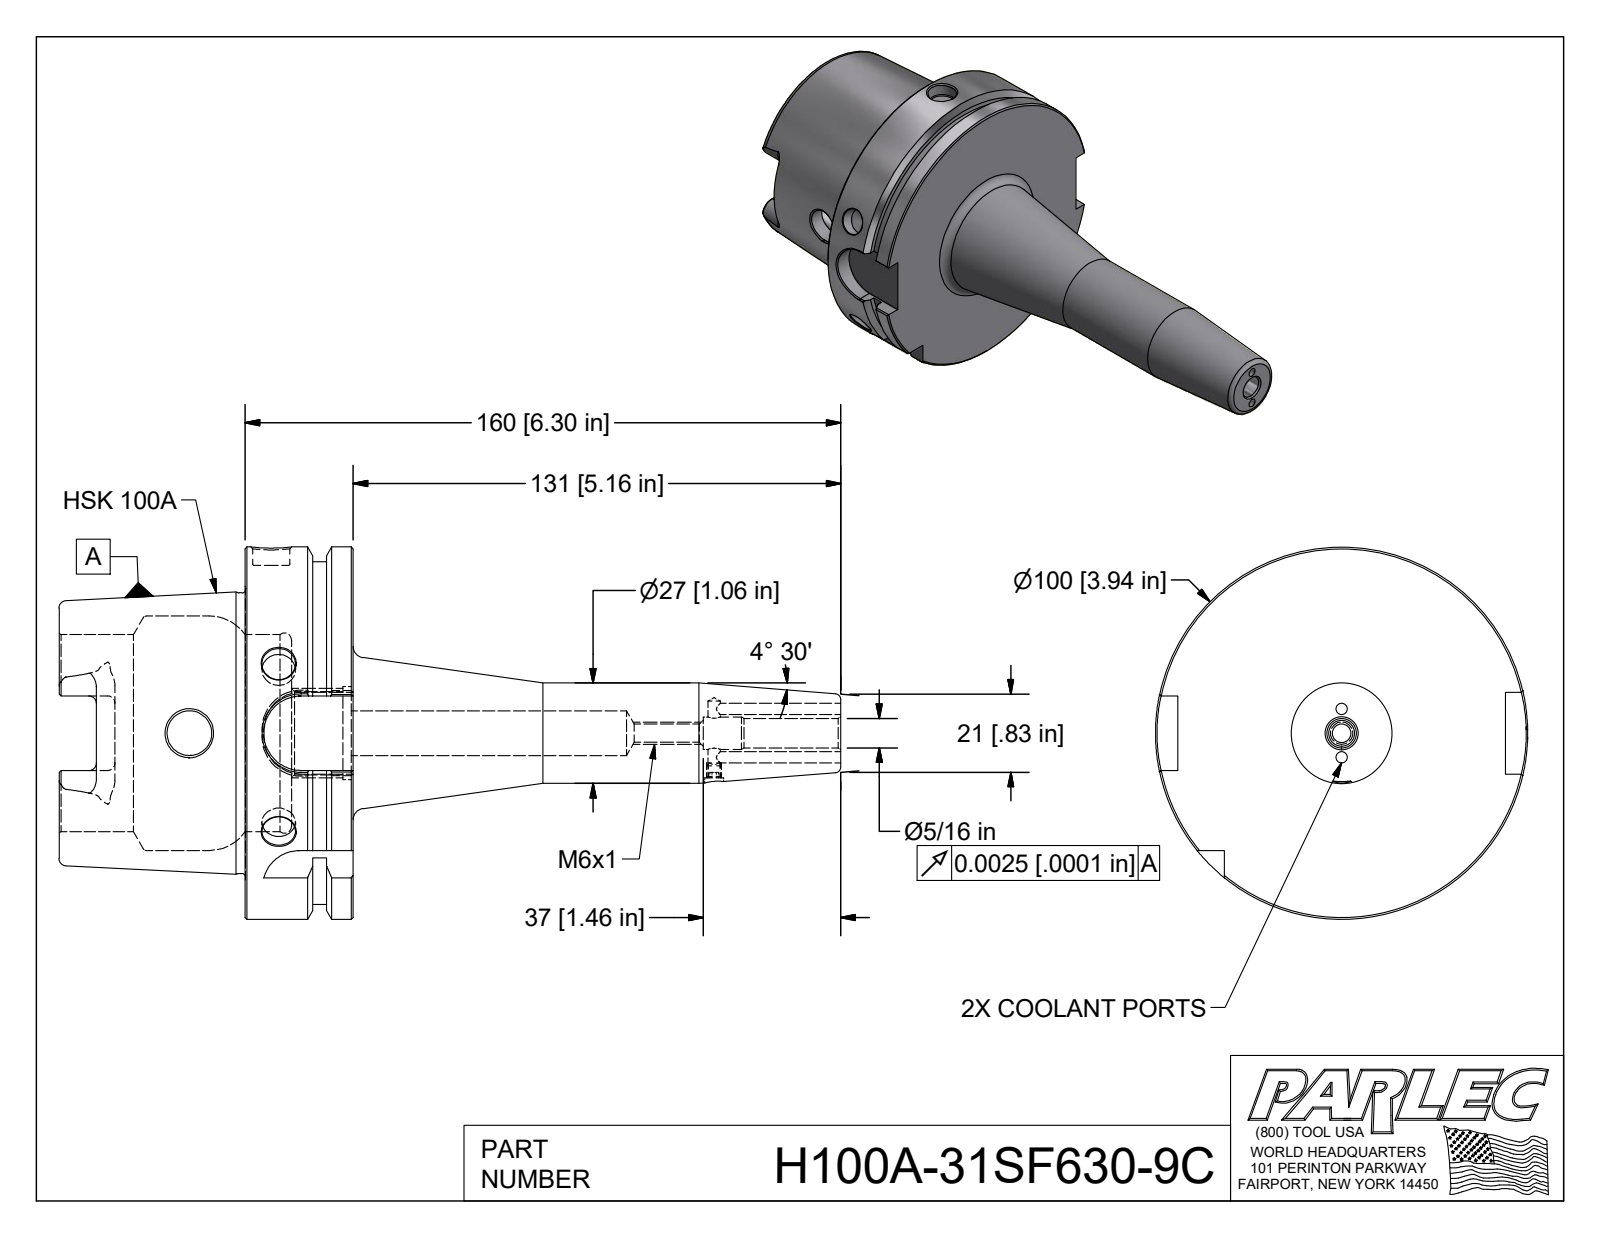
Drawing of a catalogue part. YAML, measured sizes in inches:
step_written_by: "Autodesk Inventor 2018 (AUTOMOTIVE_DESIGN)"
units: inches
bodies: {solids: 1, faces: 150, planar: 49, cylindrical: 42, other: 59}
overall_size: [8.269, 3.937, 3.937]
volume: 20.23
surface_area: 101.6
round_holes:
  - {diameter: 0.118, count: 2}
  - {diameter: 0.354, count: 2}
  - {diameter: 0.128, count: 1}
  - {diameter: 0.194, count: 1}
  - {diameter: 0.197, count: 1}
  - {diameter: 0.312, count: 1}
  - {diameter: 0.342, count: 1}
  - {diameter: 0.394, count: 1}
  - {diameter: 0.472, count: 1}
  - {diameter: 0.472, count: 1}
  - {diameter: 0.881, count: 1}
  - {diameter: 0.985, count: 1}
round_bosses_or_shafts:
  - {diameter: 3.937, count: 1}
  - {diameter: 3.622, count: 1}
  - {diameter: 2.967, count: 1}
  - {diameter: 1.063, count: 1}
partial_cylinders:
  - {radius: 0.079, count: 6}
  - {radius: 0.192, count: 4}
  - {radius: 0.394, count: 4}
face_to_face_distances: [1.142, 0.492, 0.65, 1.969, 2.461, 3.11, 3.465, 2.83, 0.861, 0.369]
hole_center_spacings: [0.256, 0.512, 4.684]
